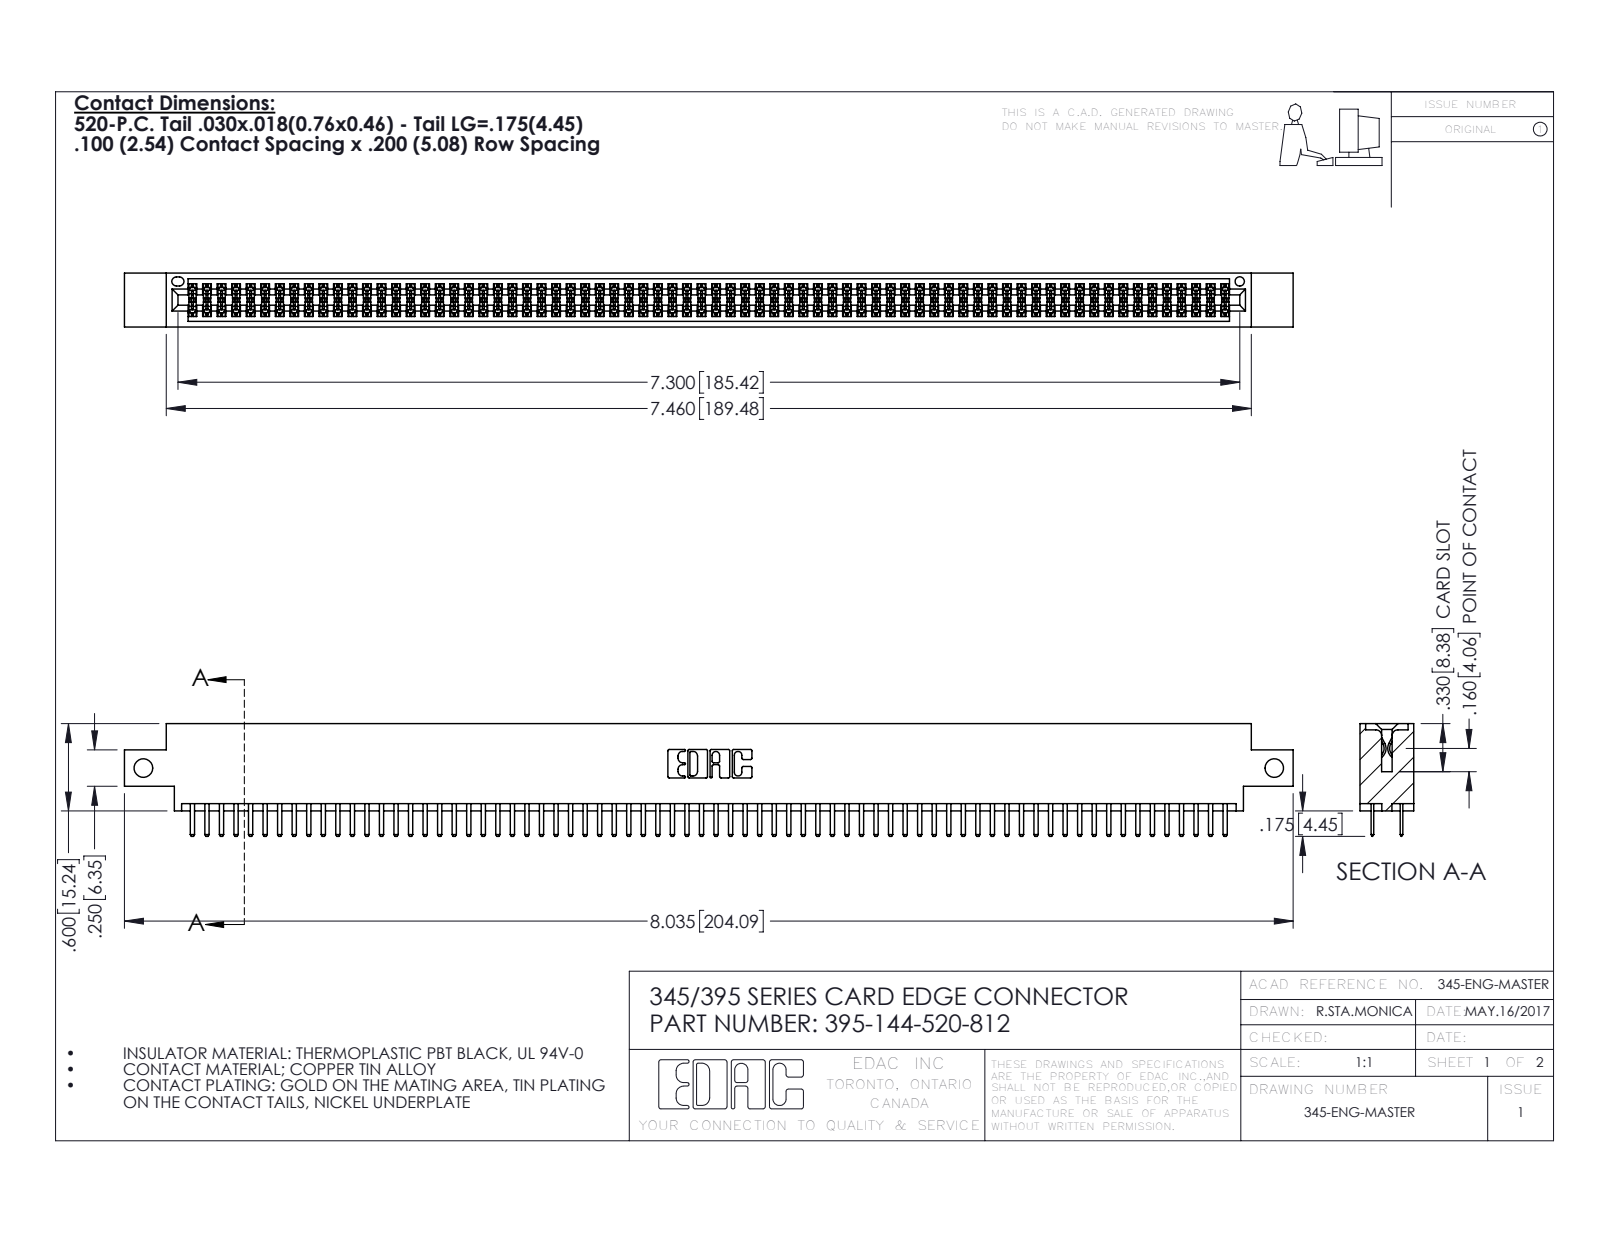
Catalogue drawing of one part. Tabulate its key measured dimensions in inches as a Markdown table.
| quantity | value |
| --- | --- |
| part name | 345 Part_0.170 Offset - Side Mount; 345-292-001_345-293-120; 395-144-520-812 |
| STEP written by | SolidWorks 2016 (CONFIG_CONTROL_DESIGN) |
| units | inches |
| bodies | 145 solids, 7906 faces (5124 planar, 2782 cylindrical, 0 other) |
| overall size | 8.035 × 0.775 × 0.37 |
| volume | 1.211 in³ |
| surface area | 46.16 in² |
| round holes (diameter × count) | 0.128 × 2, 0.064 × 1 |
| partial cylindrical surfaces (radius × count) | 0.006 × 216, 0.01 × 148, 0.01 × 22, 0.007 × 6, 0.031 × 6, 0.026 × 3, 0.014 × 2, 0.019 × 2 |
| main face-to-face distances | 0.072, 0.298, 0.2, 0.37, 0.098, 0.272, 0.025, 0.225, 0.022, 0.072 |
| hole center spacings | 7.775 |
